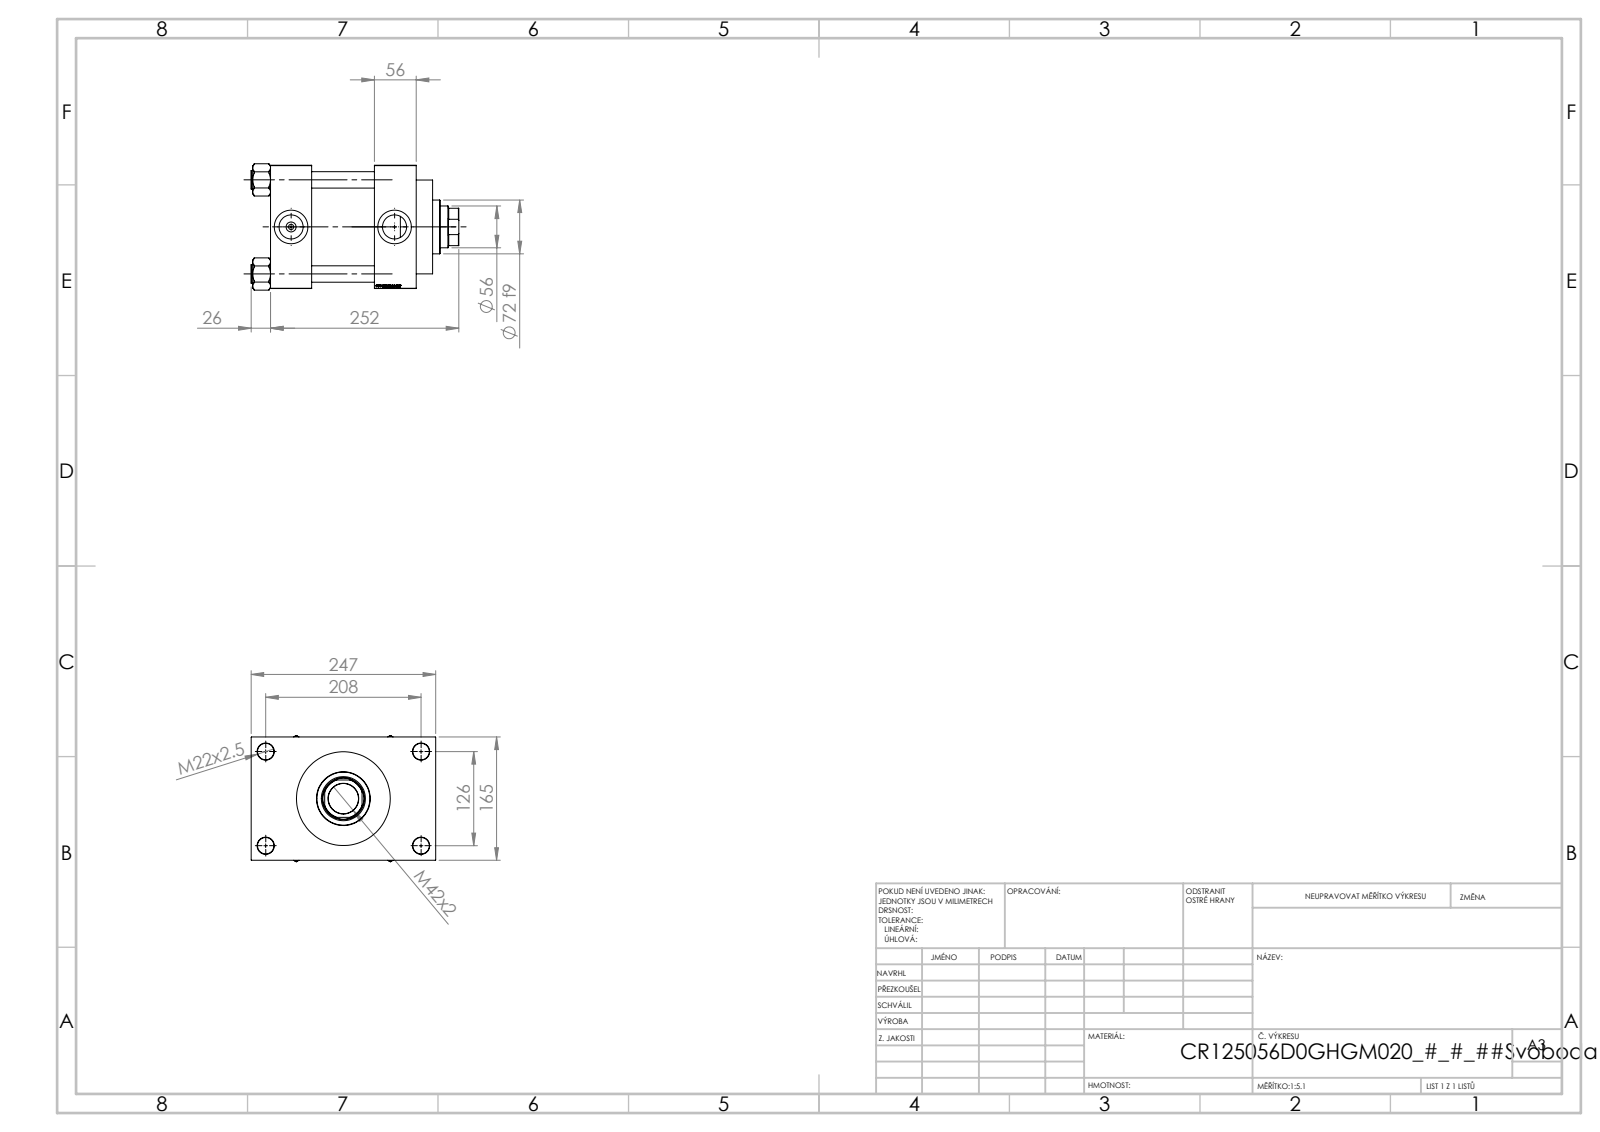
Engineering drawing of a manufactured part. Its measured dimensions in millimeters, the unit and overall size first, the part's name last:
Units: millimetres
Overall size (bounding box): 278 × 247 × 169.14
Round holes (diameter × count): ⌀22 ×8, ⌀7 ×2, ⌀32.24 ×2, ⌀45 ×2, ⌀40.5 ×1, ⌀56 ×1, ⌀59 ×1, ⌀96 ×1, ⌀125 ×1, ⌀125.5 ×1
Round bosses / shafts (diameter × count): ⌀25 ×4, ⌀131 ×1, ⌀72 ×1
Partial cylindrical surfaces — rounded edges, fillets, slot ends (radius × count): R27 ×1
Main face-to-face distances: 165, 84, 55, 139, 56, 195, 140, 41, 206, 173.74
Hole centre spacings: 41.05, 89.02, 121.59, 125.9, 132.47, 166.95, 209.13, 126
Volume: 4 924 000 mm³ · Surface area: 534 057 mm²
Bodies: 11 solids, 1148 faces (544 planar, 86 cylindrical, 518 other)
Part name (STEP PRODUCT): V215CR_VCP_D; V215CR_D_Body; V215_VC_A; NUT_M5_D (+1 more)
STEP written by: SolidWorks 2019 (CONFIG_CONTROL_DESIGN)
